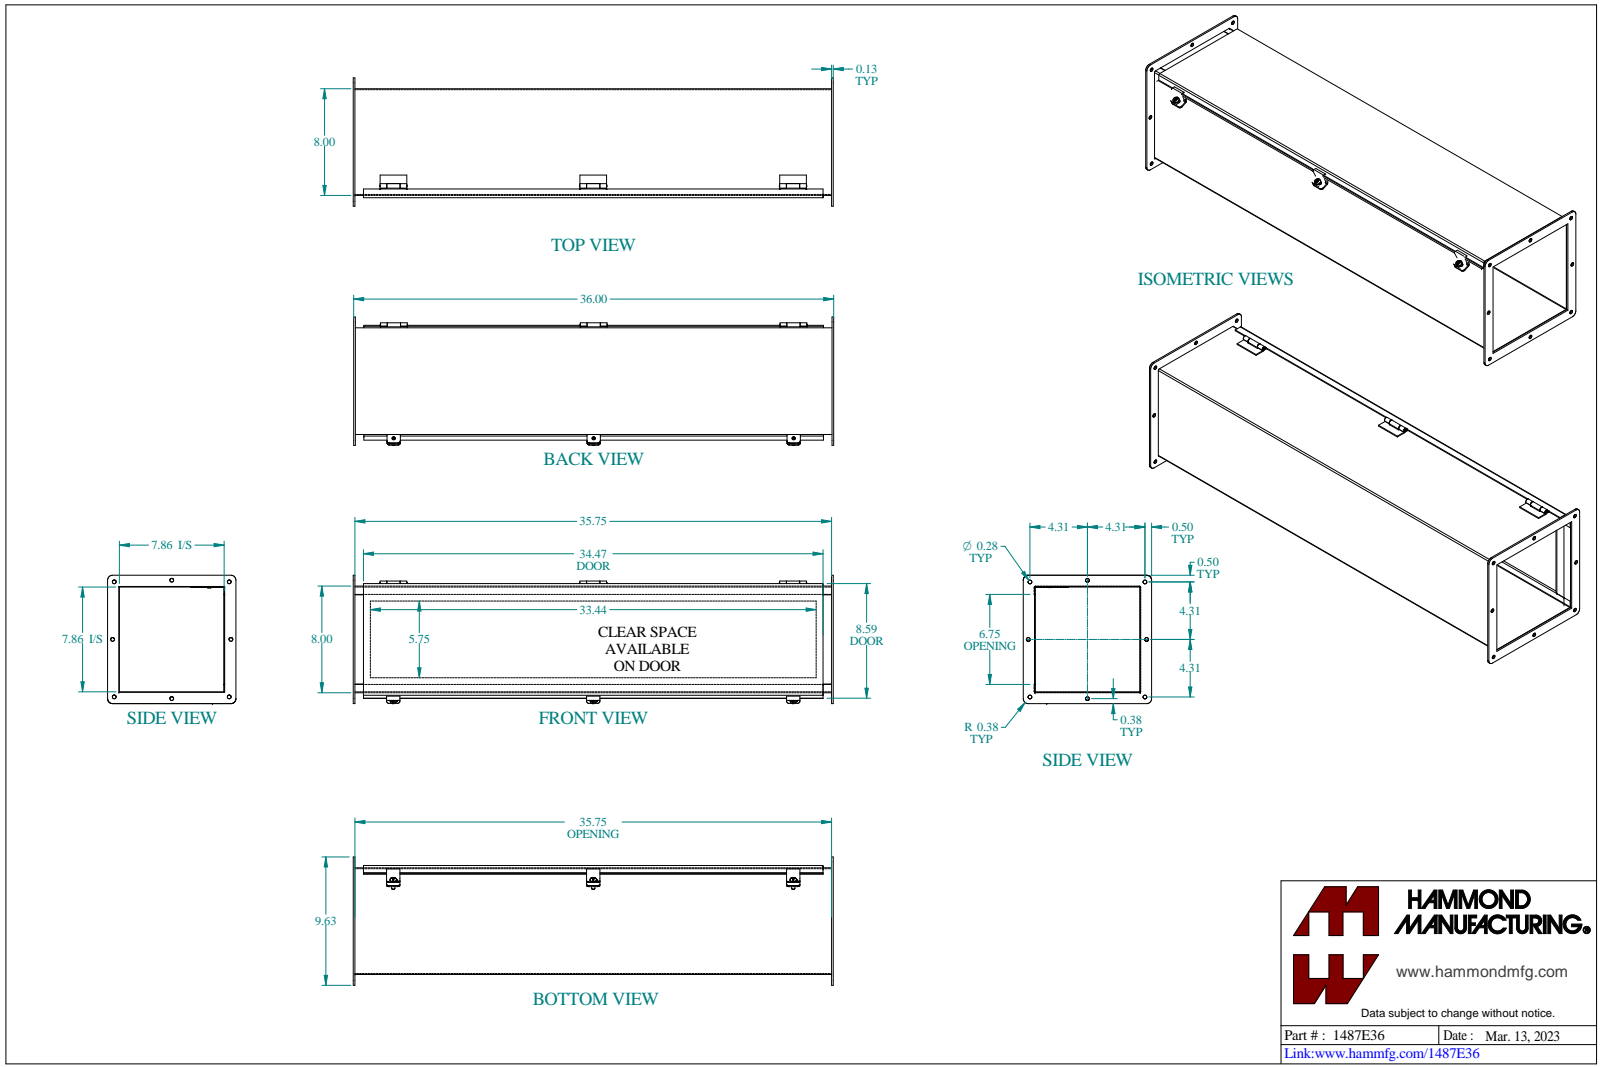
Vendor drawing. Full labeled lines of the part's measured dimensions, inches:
Part name (STEP PRODUCT): 1487E36
STEP written by: SolidWorks 2023 (CONFIG_CONTROL_DESIGN)
Units: inches
Bodies: 25 solids, 560 faces (299 planar, 204 cylindrical, 57 other)
Overall size (bounding box): 36.125 × 9.631 × 9.625
Volume: 102 in³ · Surface area: 2 755 in²
Round holes (diameter × count): ⌀0.281 ×16, ⌀0.213 ×3, ⌀0.125 ×1
Round bosses / shafts (diameter × count): ⌀0.48 ×3, ⌀0.246 ×3, ⌀0.275 ×1, ⌀0.125 ×1
Partial cylindrical surfaces — rounded edges, fillets, slot ends (radius × count): R0.188 ×12, R0.375 ×8, R0.036 ×7, R0.108 ×7, R0.01 ×6, R0.141 ×6, R0.25 ×4, R0.029 ×2
Main face-to-face distances: 0.072, 7.928, 8.1, 8, 7.856, 8.172, 8.028, 0.172, 0.125, 35.875
Hole centre spacings: 4.315, 9.755, 8.625, 6.276, 8.875, 4.311, 4.314, 4.318
